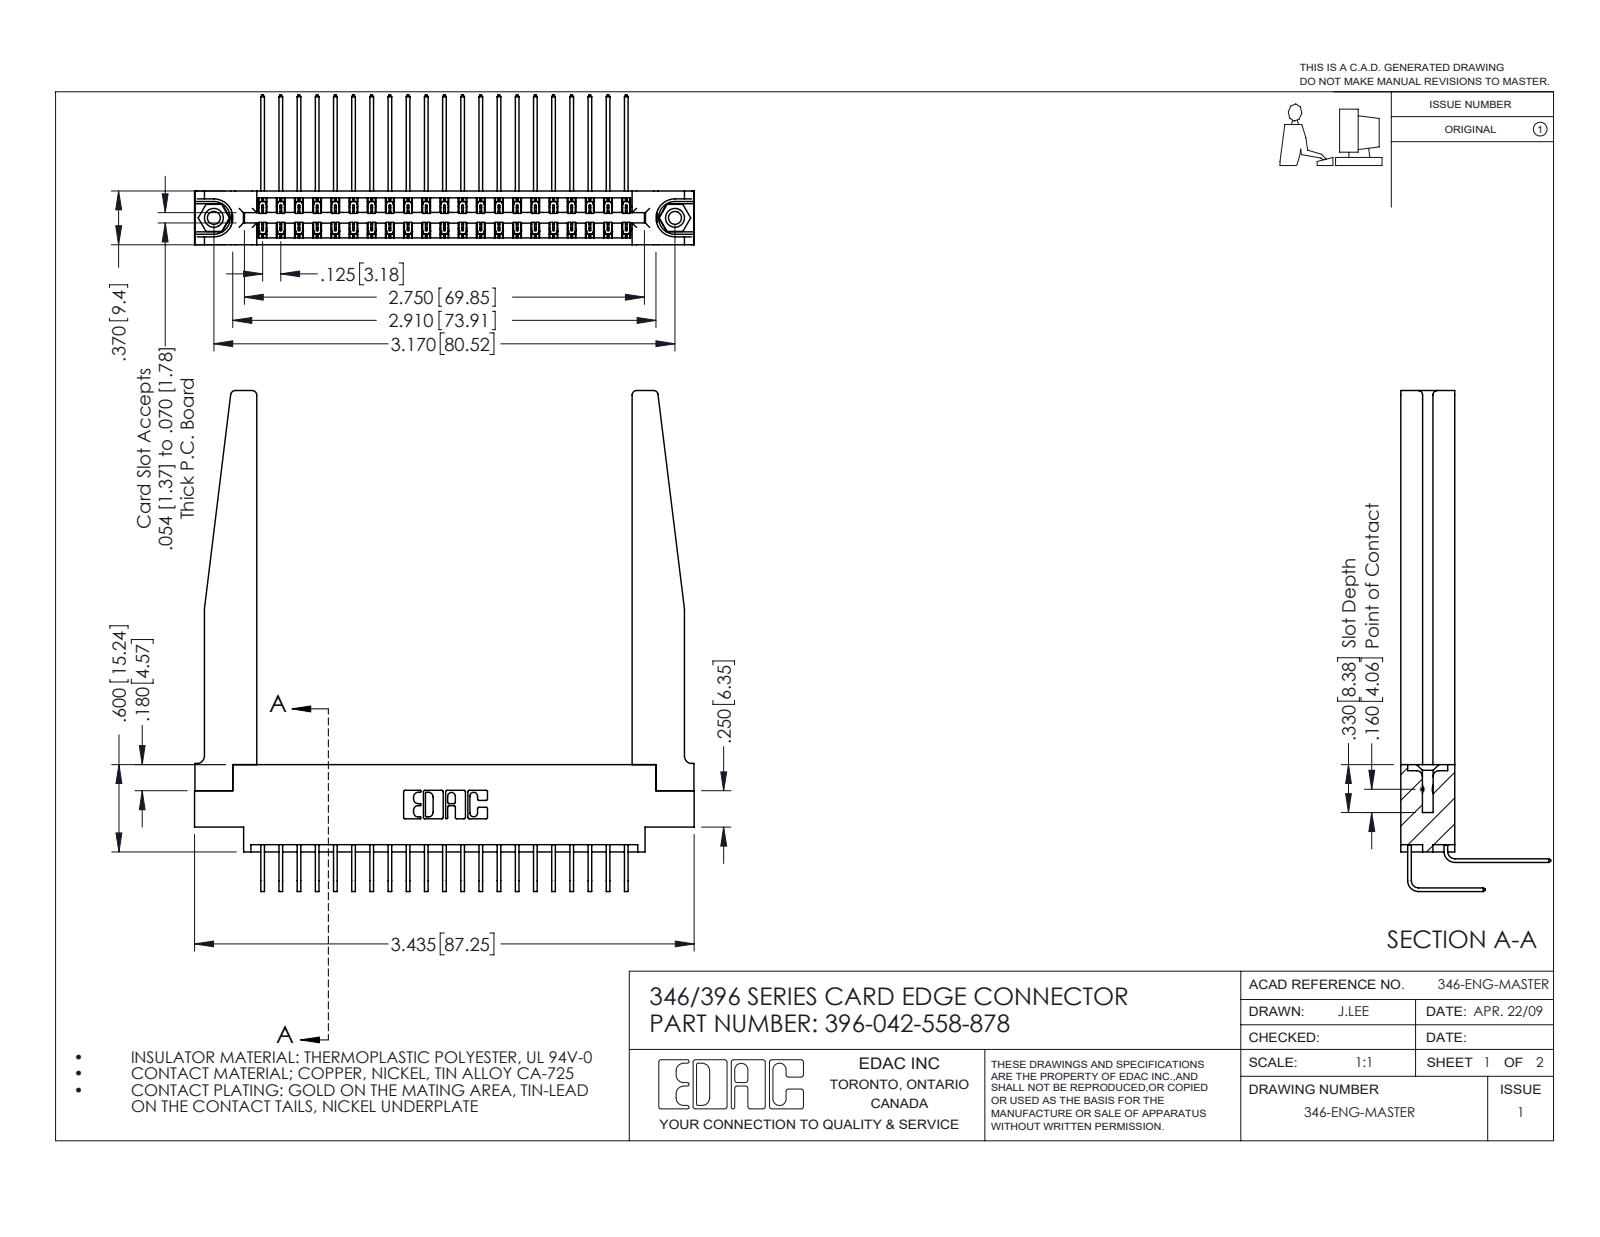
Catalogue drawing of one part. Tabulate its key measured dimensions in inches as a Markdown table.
| quantity | value |
| --- | --- |
| part name | 345-250-001_345-250-001-102; 346 Part_0.170 Offset - 0.156 Dia-TH; 345-292-001_558 559 Tail - 1; 345-292-001_558 Tail - 2 (+2 more) |
| STEP written by | SolidWorks 2016 (CONFIG_CONTROL_DESIGN) |
| units | inches |
| bodies | 47 solids, 2628 faces (1776 planar, 800 cylindrical, 52 other) |
| overall size | 3.443 × 3.435 × 1.03 |
| volume | 0.936 in³ |
| surface area | 29.67 in² |
| round holes (diameter × count) | 0.089 × 2, 0.125 × 2, 0.156 × 2, 0.064 × 1 |
| round bosses / shafts (diameter × count) | 0.155 × 2 |
| partial cylindrical surfaces (radius × count) | 0.006 × 63, 0.01 × 22, 0.03 × 8, 0.007 × 6, 0.031 × 6, 0.05 × 4, 0.026 × 3, 0.014 × 2 |
| main face-to-face distances | 0.37, 0.322, 0.048, 0.072, 0.148, 0.15, 0.025, 0.25, 0.298, 0.275 |
| hole center spacings | 0.246, 2.963, 3.17 |
